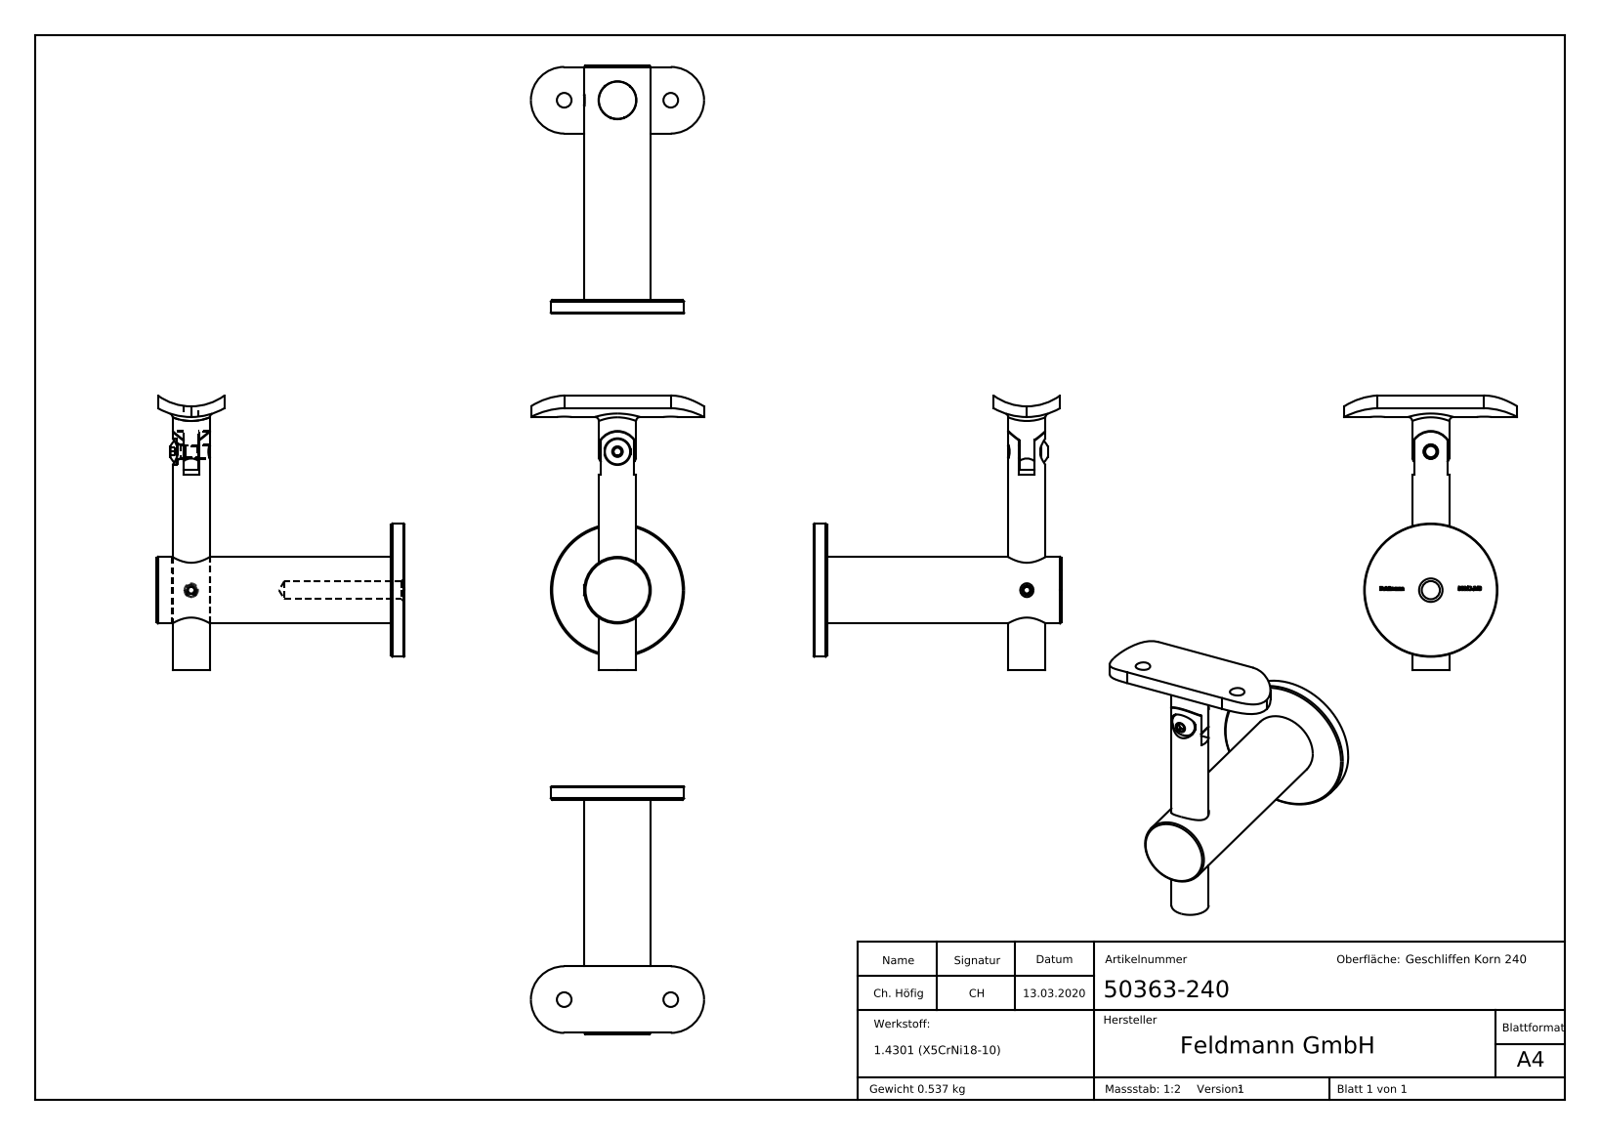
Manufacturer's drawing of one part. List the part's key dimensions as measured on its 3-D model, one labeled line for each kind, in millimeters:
Part name (STEP PRODUCT): 503XX-240 Teil1; DIN913; DIN 7380_DIN 7380 M5x12; DIN913_DIN 913 M5x5 (+7 more)
STEP written by: SolidWorks 2015 (CONFIG_CONTROL_DESIGN)
Units: millimetres
Bodies: 5 solids, 319 faces (152 planar, 28 cylindrical, 139 other)
Overall size (bounding box): 103.08 × 93 × 88
Volume: 67 968 mm³ · Surface area: 22 842 mm²
Round holes (diameter × count): ⌀5.5 ×3, ⌀4.2 ×2, ⌀6.8 ×1, ⌀10 ×1, ⌀14.2 ×1
Round bosses / shafts (diameter × count): ⌀5 ×2, ⌀50 ×1, ⌀25 ×1, ⌀14 ×1, ⌀9.5 ×1
Partial cylindrical surfaces — rounded edges, fillets, slot ends (radius × count): R7.75 ×3, R12.5 ×2, R21.2 ×1, R25.2 ×1
Main face-to-face distances: 5, 93, 88, 9.5, 15.5, 9.75, 15.25, 5.75, 0.5, 92.5
Hole centre spacings: 20, 40, 52
